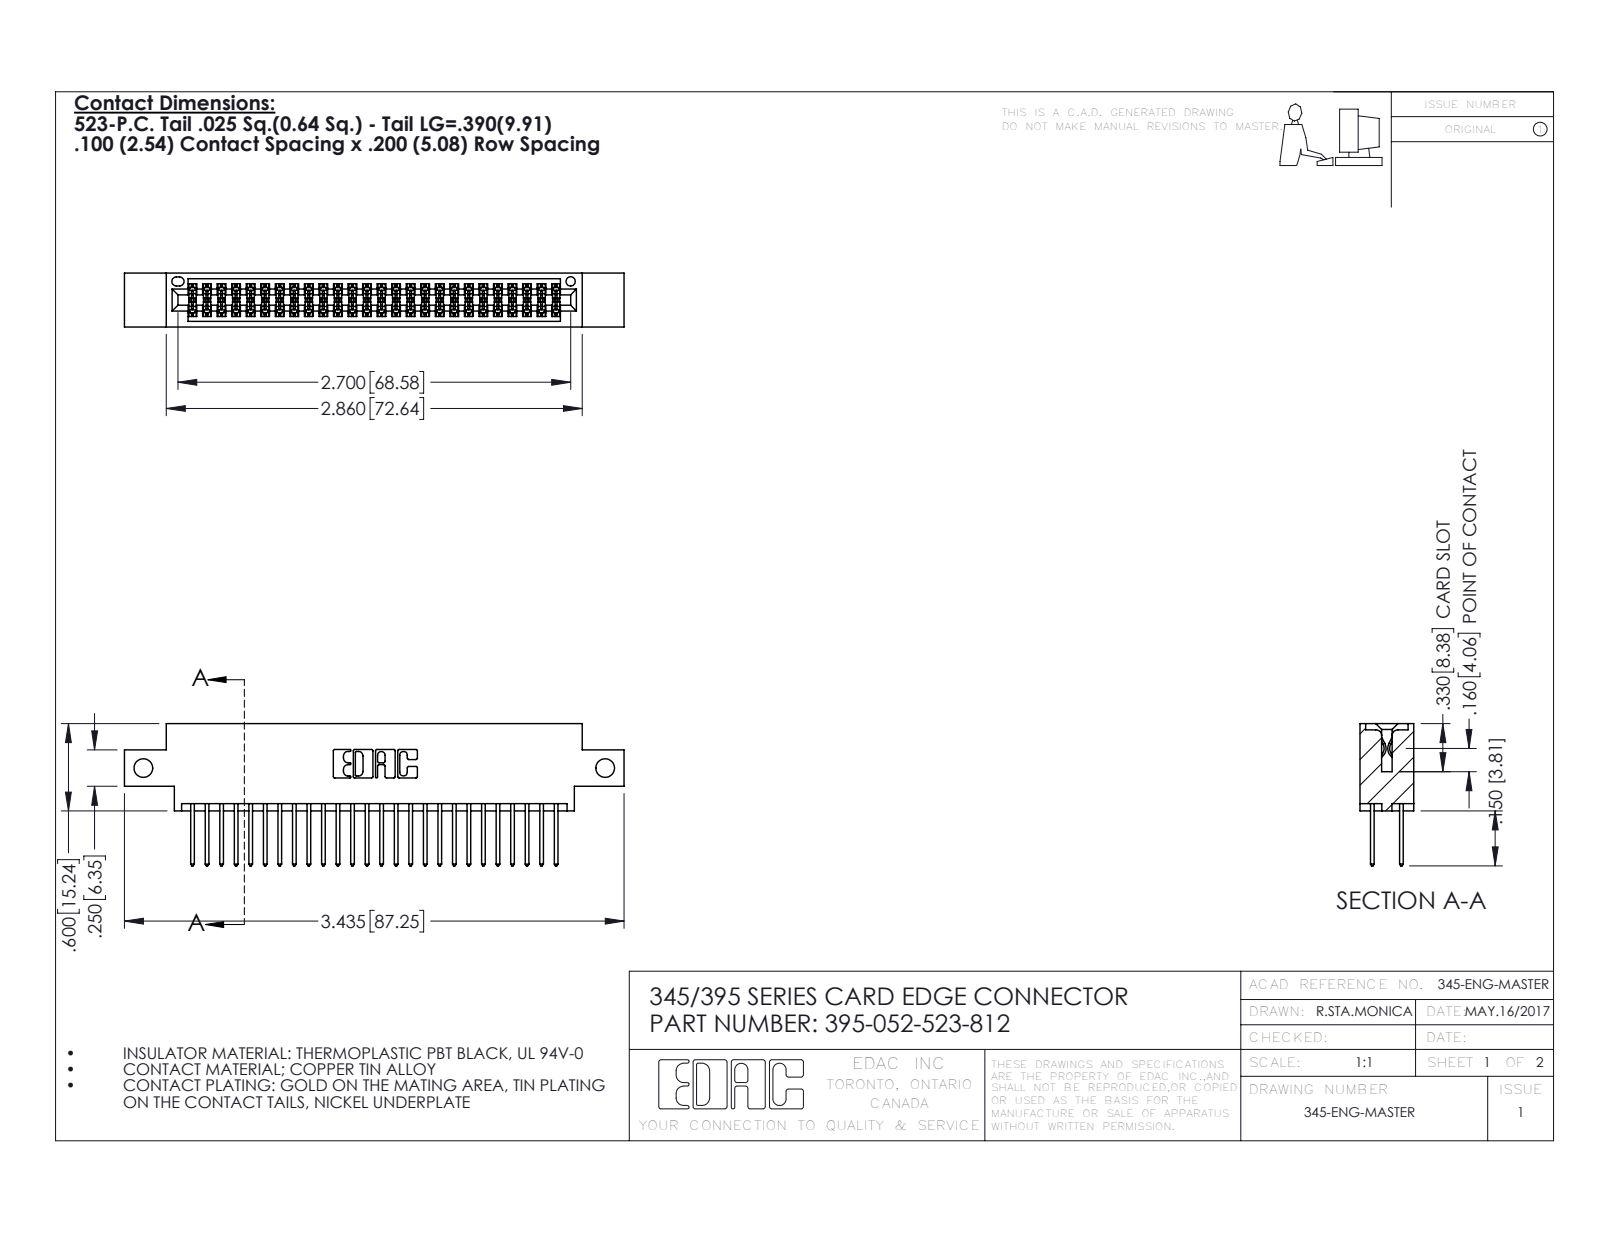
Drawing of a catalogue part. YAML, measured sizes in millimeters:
part_name: "345 Part_0.170 Offset - Side Mount; 395-052-523-812; 345-292-001_345-293-123"
step_written_by: "SolidWorks 2016 (CONFIG_CONTROL_DESIGN)"
units: millimeters
bodies: {solids: 53, faces: 2730, planar: 1800, cylindrical: 930, other: 0}
overall_size: [87.2, 24.8, 9.4]
volume: 8230
surface_area: 12350
round_holes:
  - {diameter: 3.3, count: 2}
  - {diameter: 1.6, count: 1}
partial_cylinders:
  - {radius: 0.2, count: 78}
  - {radius: 0.3, count: 52}
  - {radius: 0.3, count: 22}
  - {radius: 0.2, count: 6}
  - {radius: 0.8, count: 6}
  - {radius: 0.7, count: 3}
  - {radius: 0.4, count: 2}
  - {radius: 0.5, count: 2}
face_to_face_distances: [7.6, 1.8, 5.1, 2.5, 6.9, 0.6, 9.4, 5.7, 4.4, 3.8]
hole_center_spacings: [80.6]
